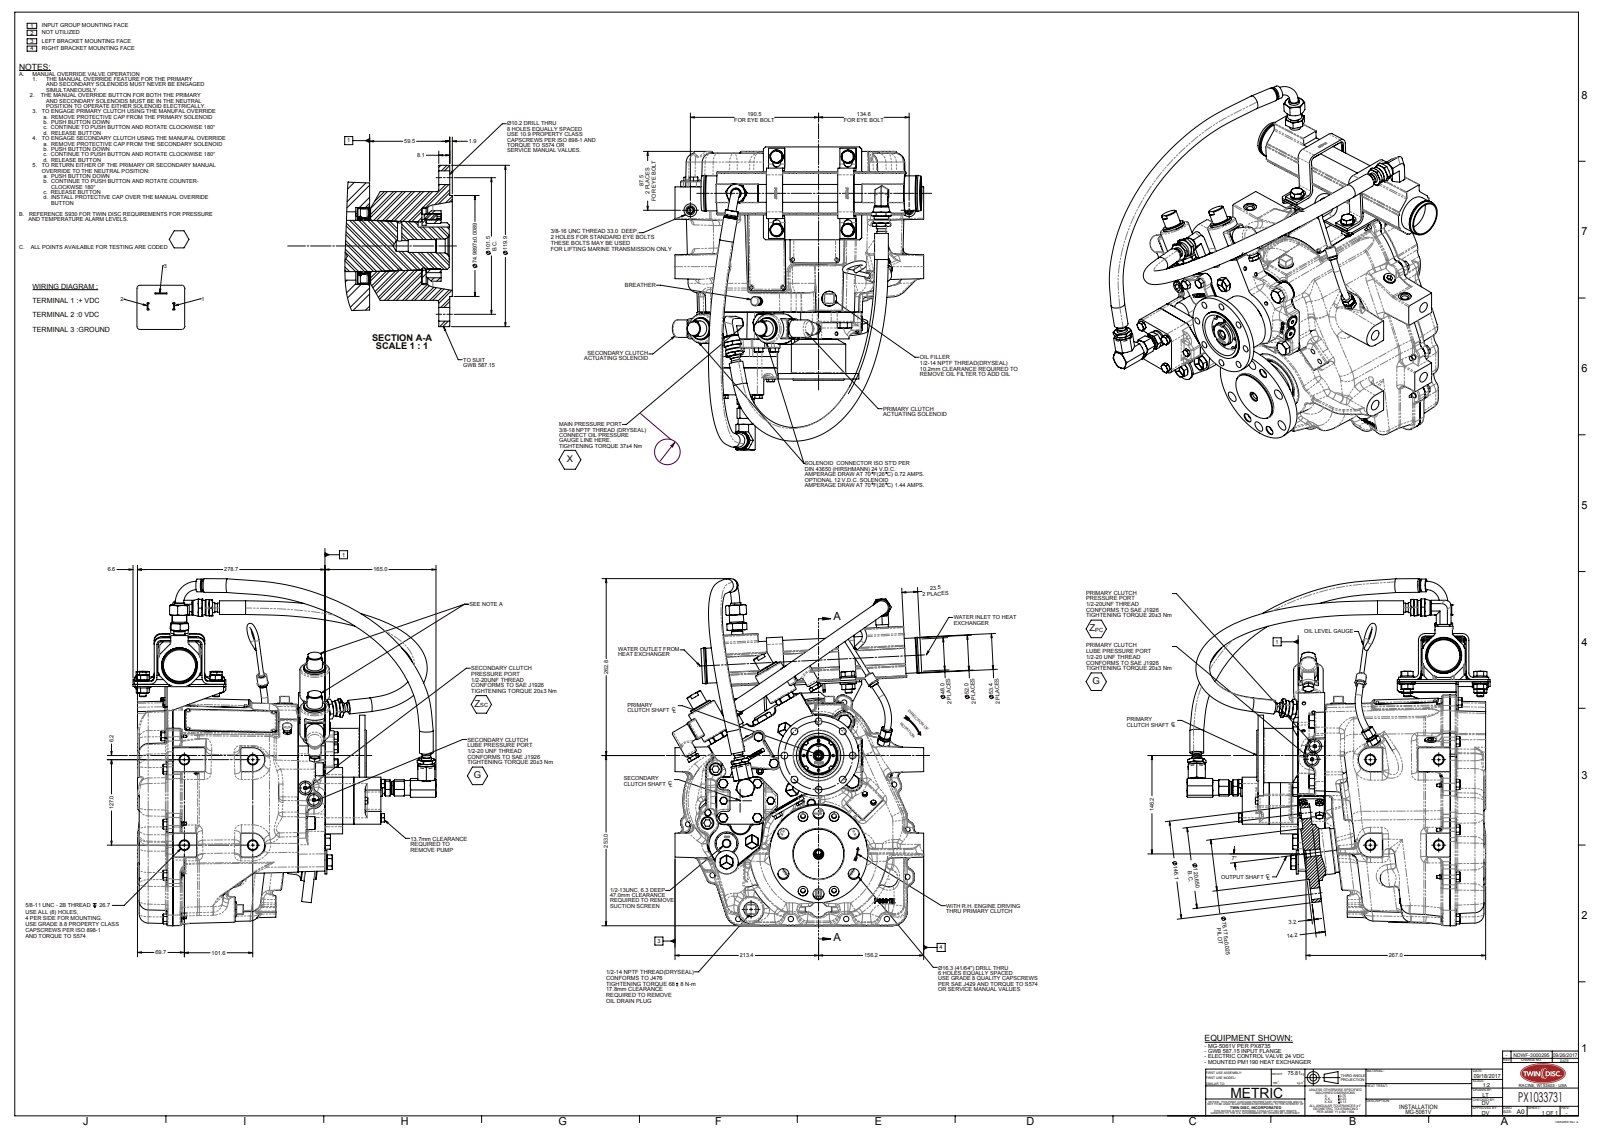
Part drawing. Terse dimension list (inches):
name: PX1033731
written by: SolidWorks 2015 (AUTOMOTIVE_DESIGN)
unit: in
bodies: 0 solids, 3155 faces (1030 planar, 706 cylindrical, 1419 other)
size: 20.308 × 17.725 × 14.706
holes: 12× ⌀0.313, 8× ⌀0.375, 8× ⌀0.402, 6× ⌀0.641, 5× ⌀0.21, 5× ⌀0.375, 4× ⌀0.281, 4× ⌀0.563, 4× ⌀0.813, 3× ⌀0.15, 3× ⌀0.625, 2× ⌀0.376
bosses: 7× ⌀0.945, 5× ⌀0.313, 4× ⌀0.803, 4× ⌀0.781, 4× ⌀0.494, 4× ⌀0.472, 4× ⌀0.394, 3× ⌀0.75
rounds: 80× R0.06, 43× R0.32, 35× R0.25, 32× R0.016, 30× R0.08, 22× R0.4, 21× R0.12, 18× R0.56
face distances: 0.031, 9.32, 9.289, 1.581, 0.12, 1.55, 10.87, 8.911, 7.361, 7.33
hole spacings: 2.562, 2.562, 4.114, 2.375, 2.375, 0.927, 2.376, 4.437
